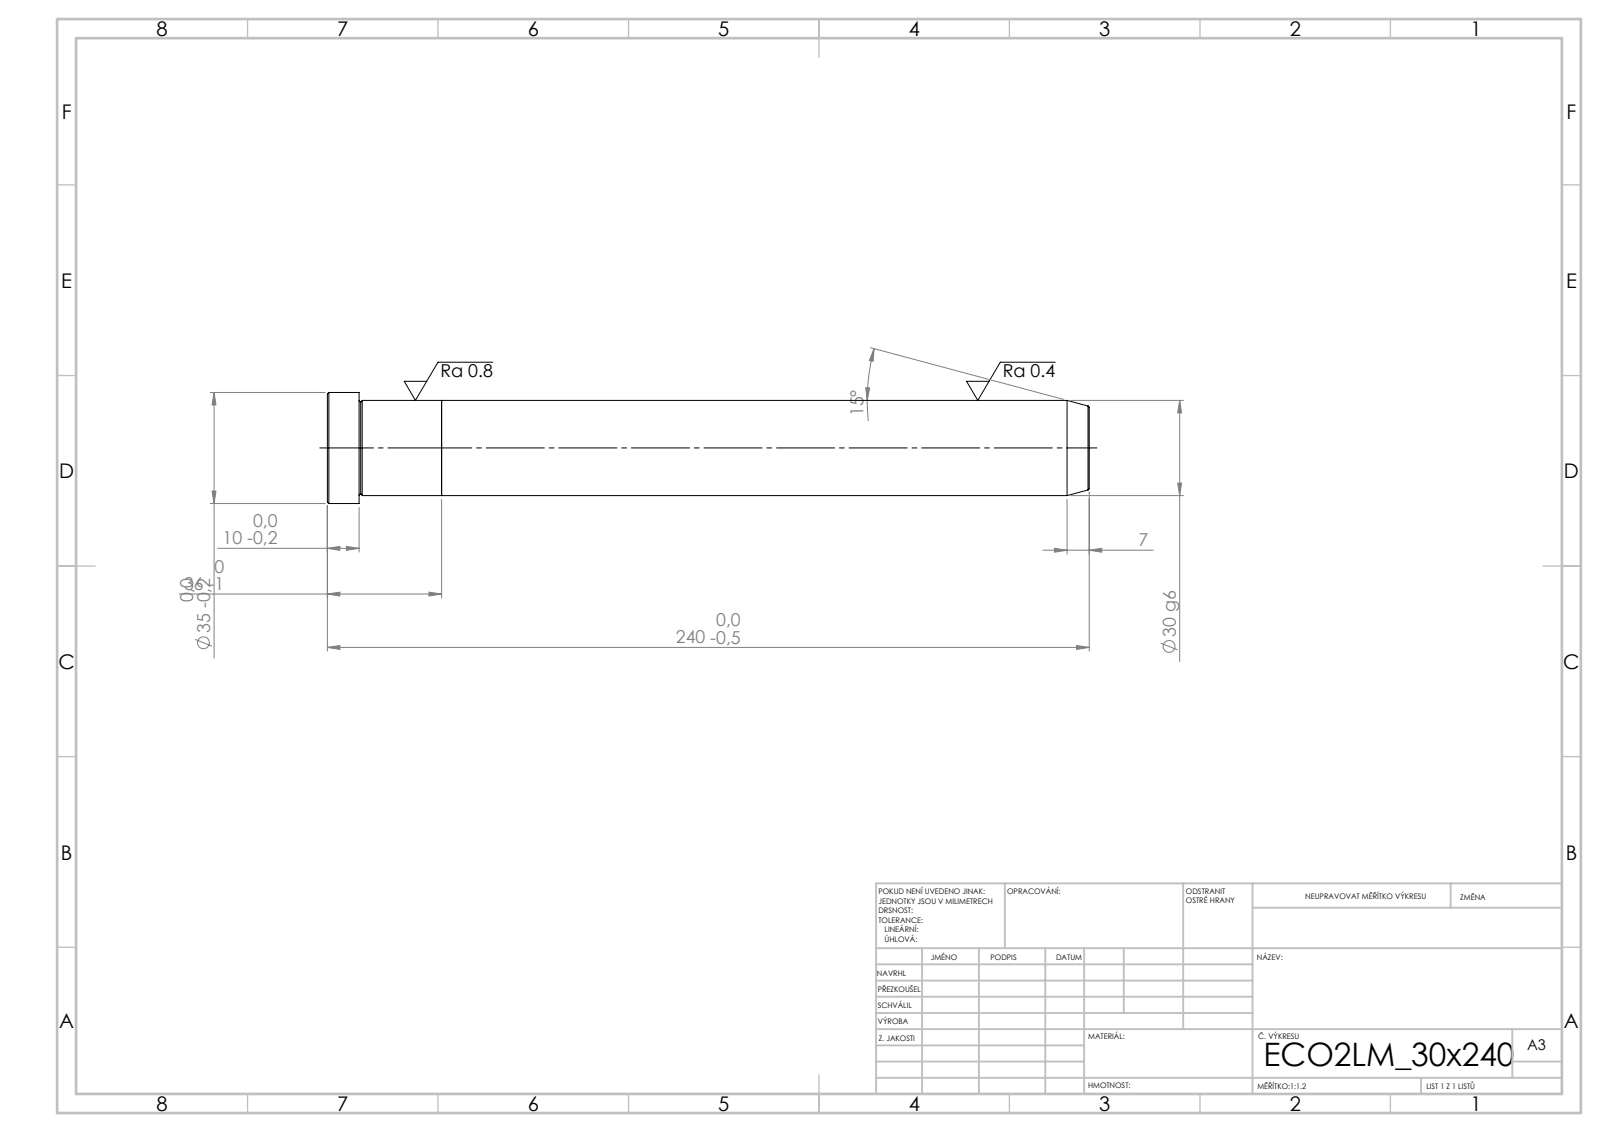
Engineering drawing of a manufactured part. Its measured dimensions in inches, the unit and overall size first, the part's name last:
Units: inches
Overall size (bounding box): 9.449 × 1.378 × 1.378
Round bosses / shafts (diameter × count): ⌀1.378 ×1, ⌀1.181 ×1
Main face-to-face distances: 1.417, 8.031, 9.449, 9.055, 1.024, 0.394
Volume: 10.47 in³ · Surface area: 40.2 in²
Bodies: 2 solids, 21 faces (5 planar, 6 cylindrical, 10 other)
STEP written by: SolidWorks 2019 (CONFIG_CONTROL_DESIGN)
